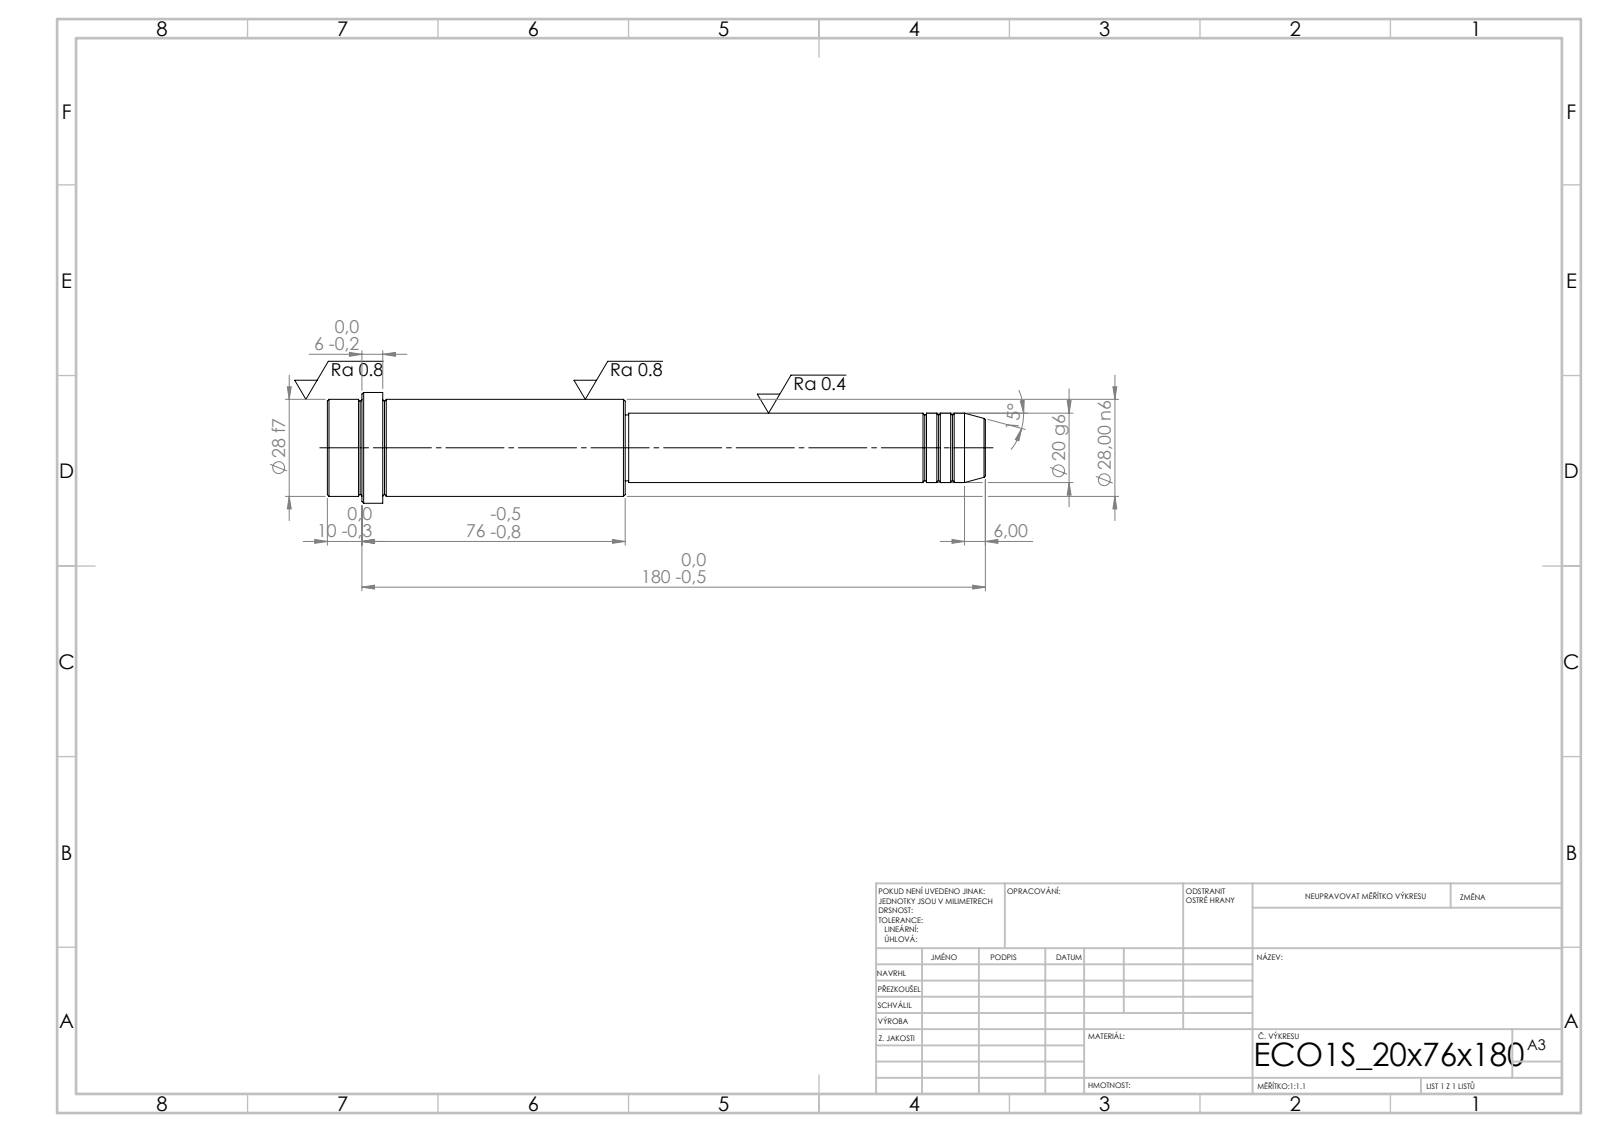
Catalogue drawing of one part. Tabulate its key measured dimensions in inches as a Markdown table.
| quantity | value |
| --- | --- |
| STEP written by | SolidWorks 2019 (CONFIG_CONTROL_DESIGN) |
| units | inches |
| bodies | 1 solid, 52 faces (6 planar, 16 cylindrical, 30 other) |
| overall size | 7.48 × 1.26 × 1.26 |
| volume | 5.264 in³ |
| surface area | 24.54 in² |
| round bosses / shafts (diameter × count) | 1.26 × 1, 1.102 × 1, 0.787 × 1, 0.748 × 1 |
| main face-to-face distances | 3.386, 4.094, 7.48, 6.85, 2.756, 0.63, 7.087, 2.992, 0.236, 0.394 |
